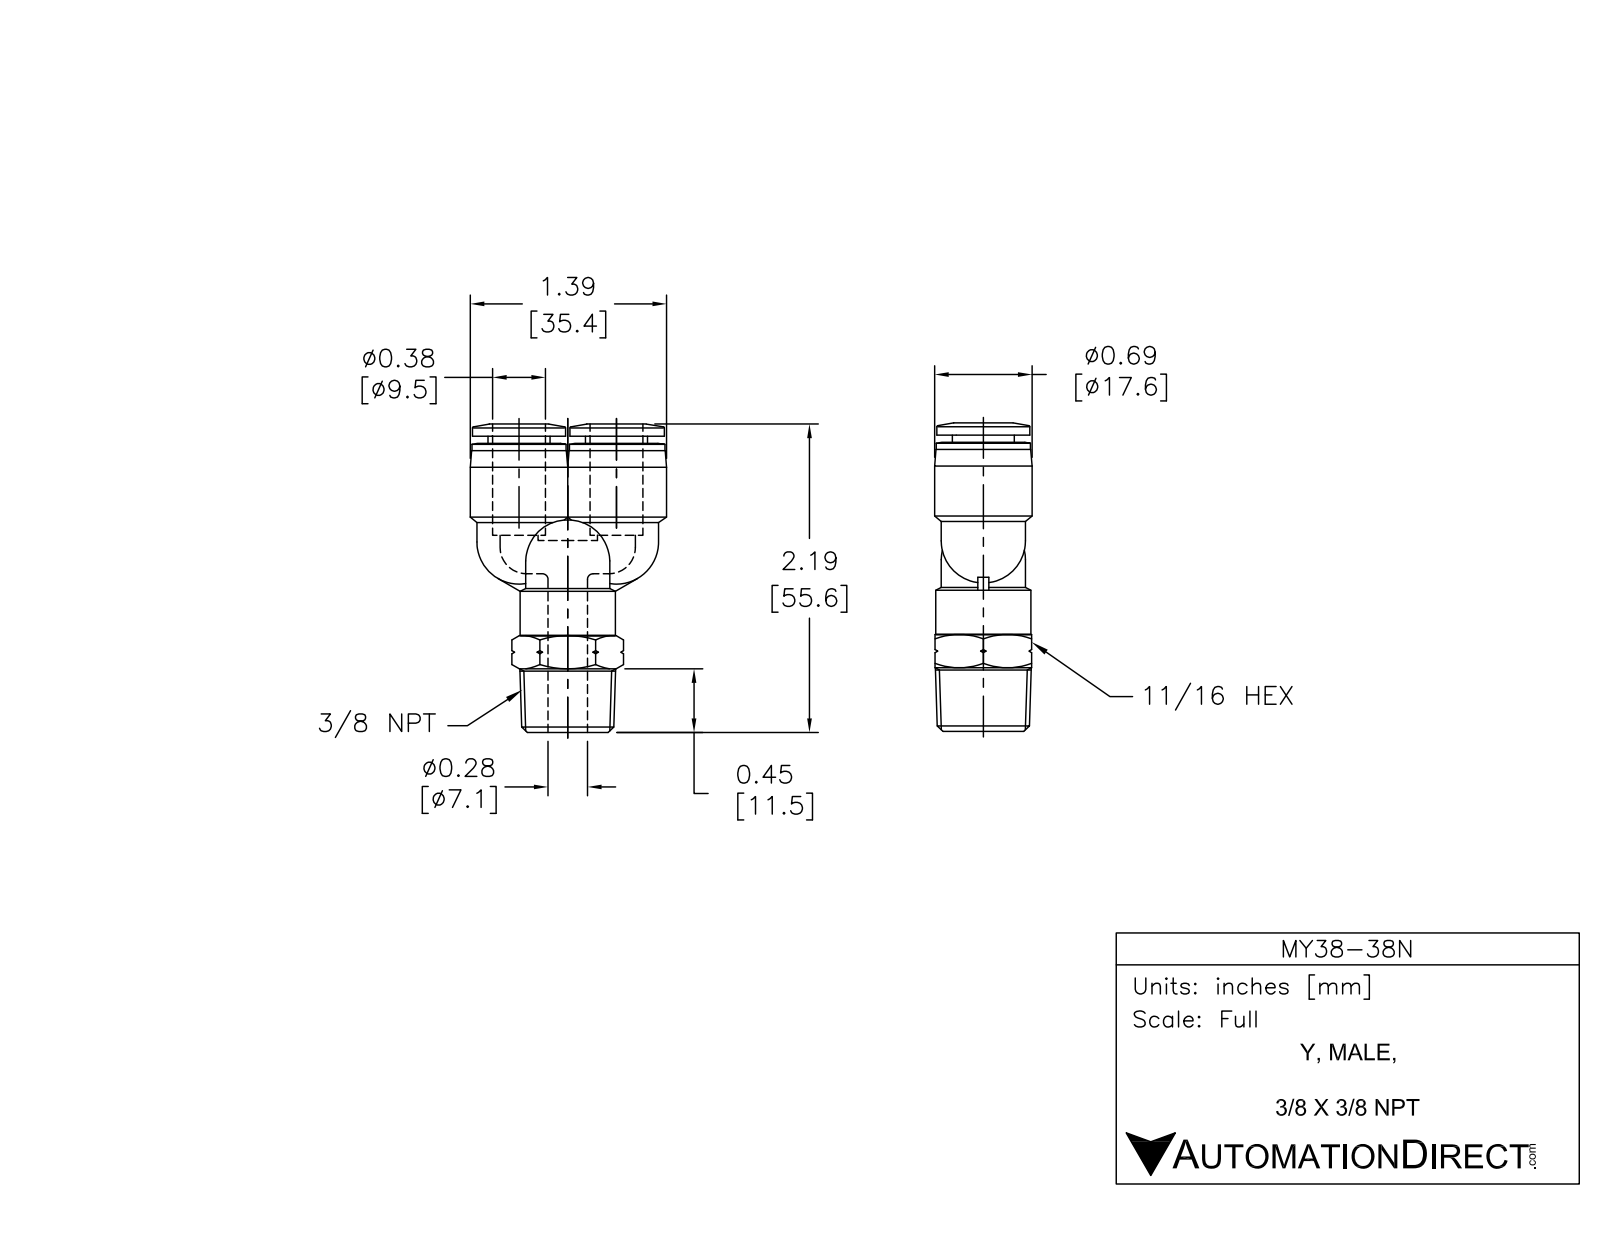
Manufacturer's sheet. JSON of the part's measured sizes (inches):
{"part_name": "MY38-38N", "step_written_by": "SolidWorks 2015 (AUTOMOTIVE_DESIGN)", "units": "inches", "bodies": {"solids": 1, "faces": 126, "planar": 22, "cylindrical": 32, "other": 72}, "overall_size": [2.193, 1.386, 0.693], "volume_in3": 0.829, "surface_area_in2": 11.82, "round_holes": [[0.386, 2], [0.276, 1]], "round_bosses_or_shafts": [[0.598, 3], [0.693, 2], [0.669, 2], [0.661, 2], [0.441, 2], [0.677, 1]], "face_to_face_distances": [0.687, 0.051, 2.055, 2.106, 0.709, 1.398, 0.657, 0.304, 0.383, 0.689], "hole_center_spacings": [0.346, 0.693]}
